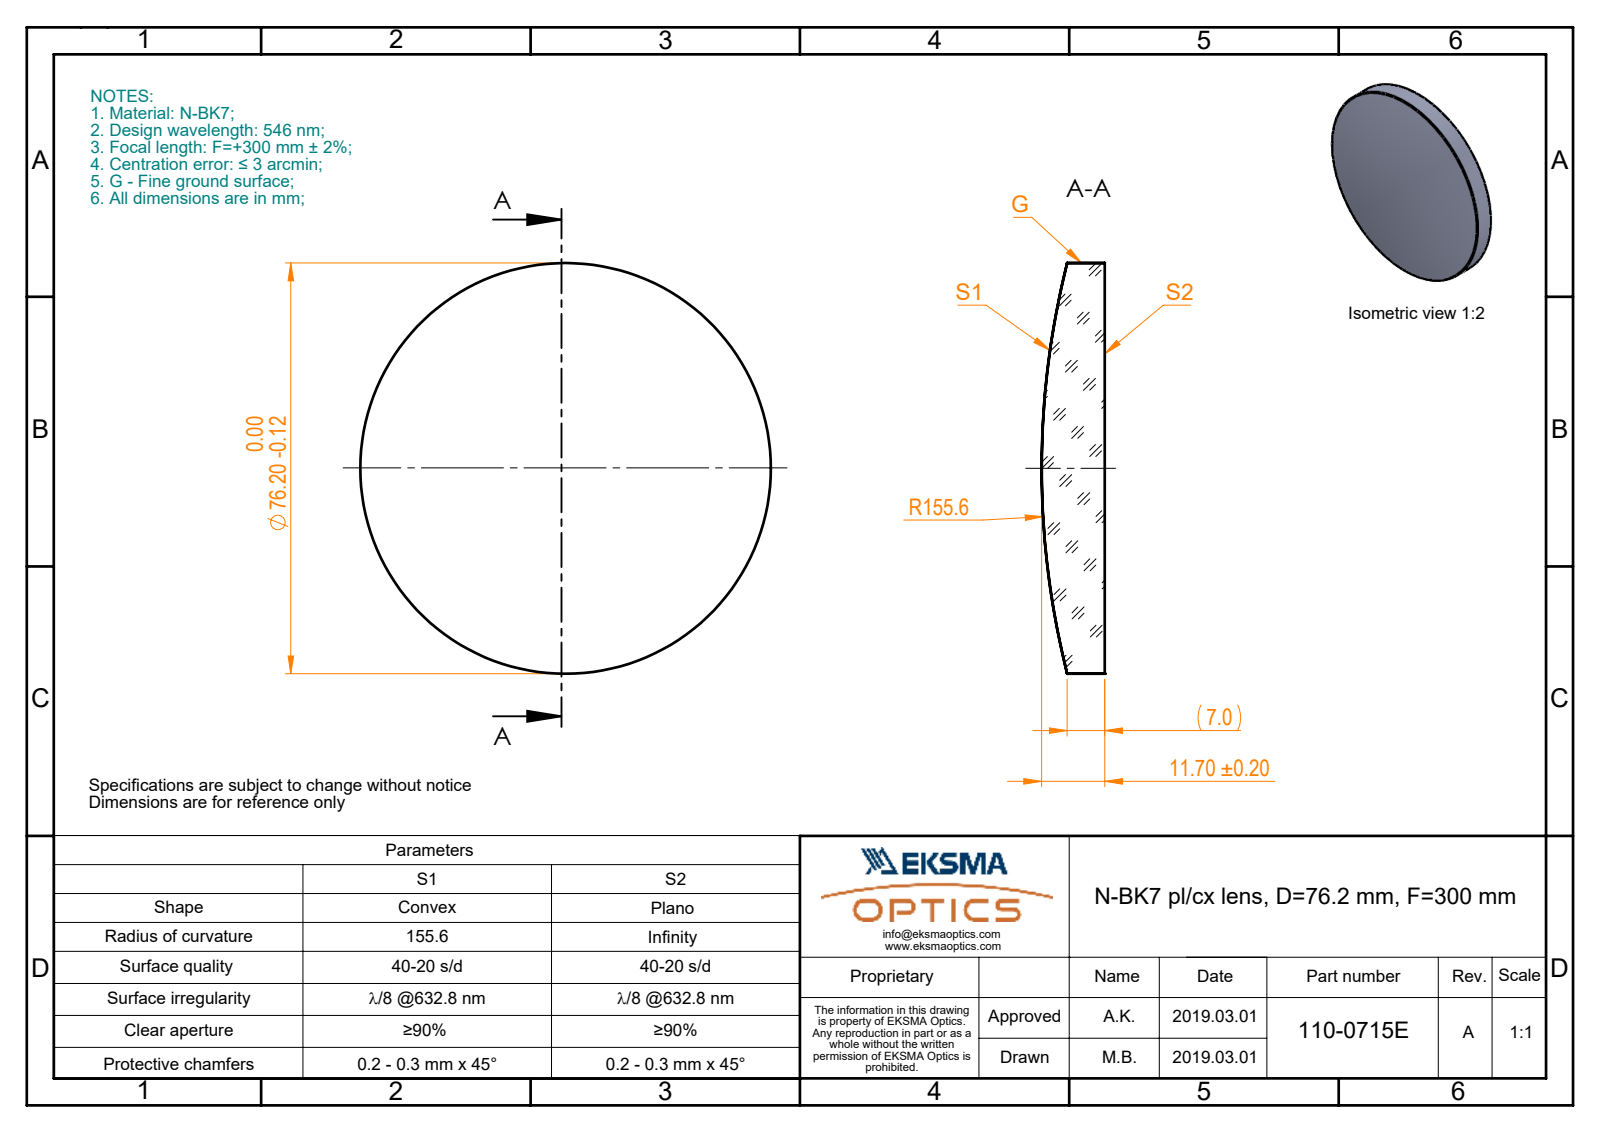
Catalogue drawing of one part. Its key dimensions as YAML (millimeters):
part_name: "110-0715E BK7 pl-cx 76.2 F300"
step_written_by: "SolidWorks 2017 (CONFIG_CONTROL_DESIGN)"
units: millimeters
bodies: {solids: 1, faces: 5, planar: 1, cylindrical: 2, other: 2}
overall_size: [76.2, 76.2, 11.7]
volume: 42612
surface_area: 10858
round_bosses_or_shafts:
  - {diameter: 76.2, count: 1}
